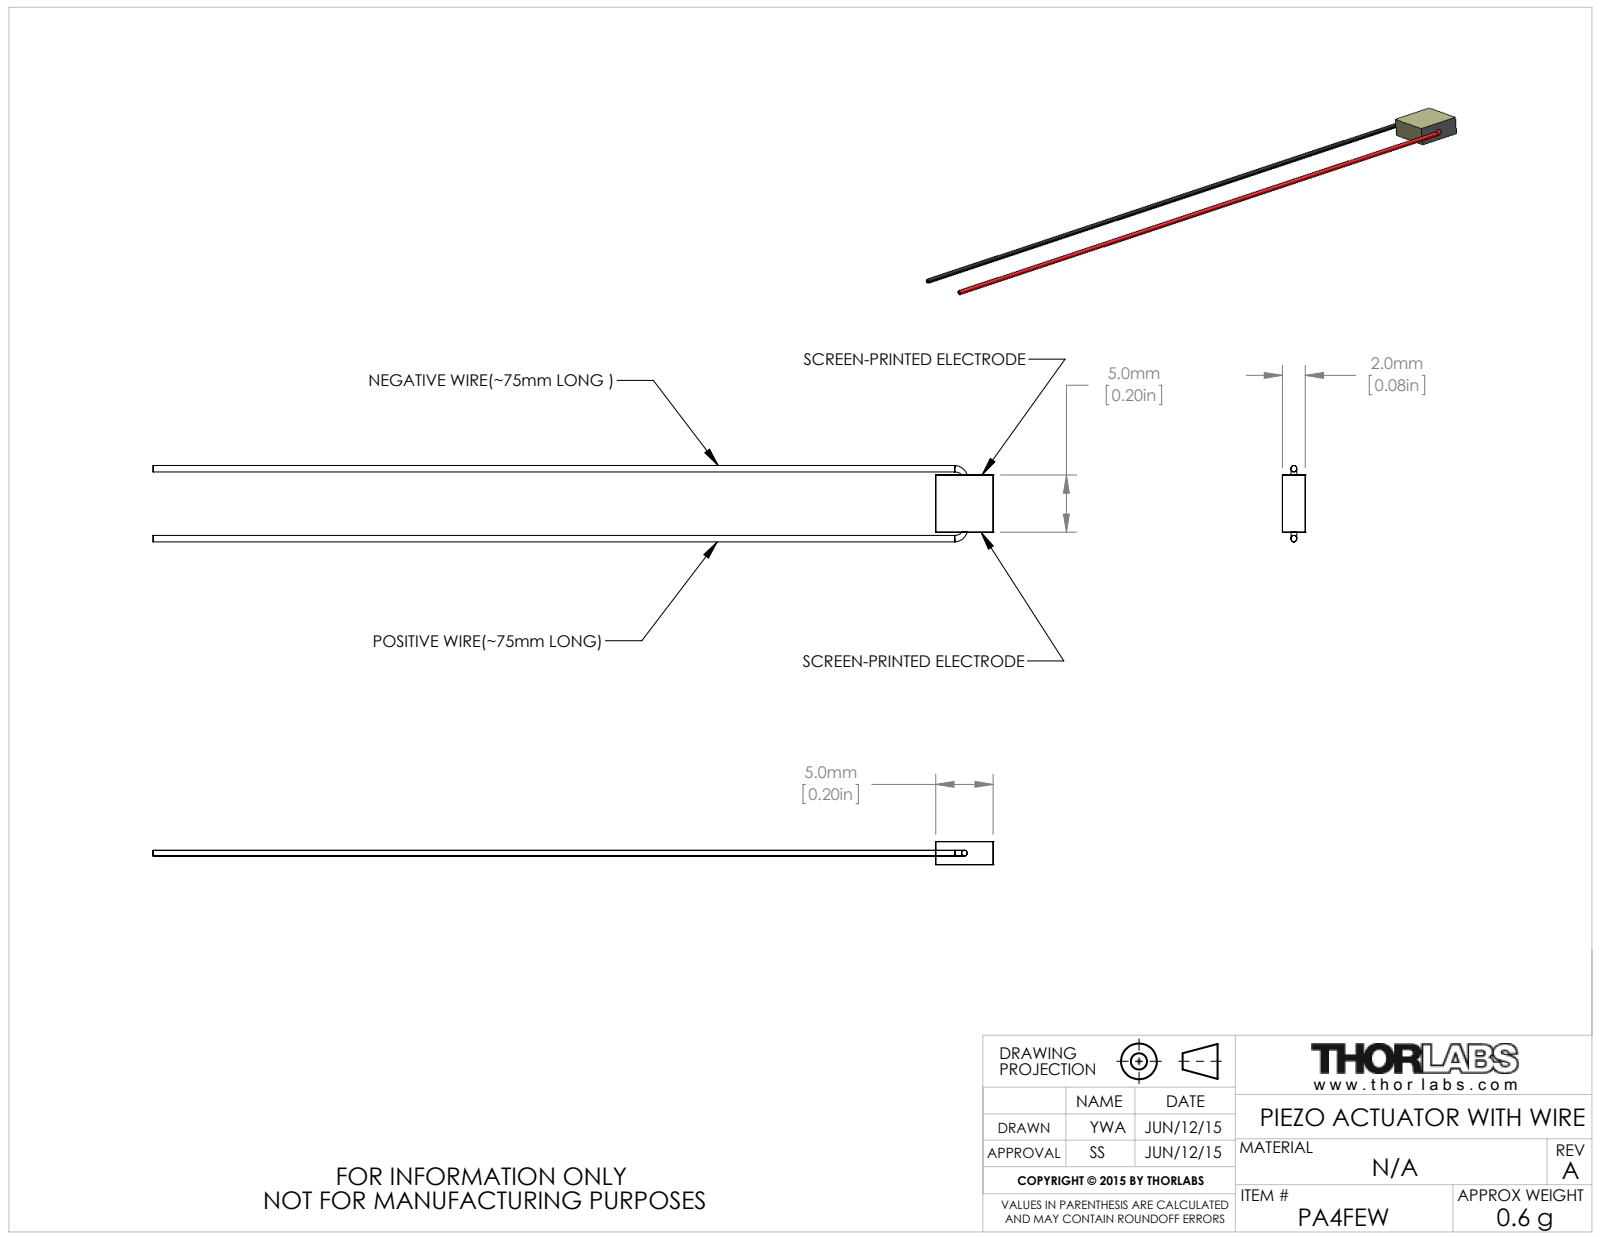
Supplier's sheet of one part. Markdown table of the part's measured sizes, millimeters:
| quantity | value |
| --- | --- |
| part name | CTN002586 |
| STEP written by | SolidWorks 2014 (AUTOMOTIVE_DESIGN) |
| units | millimeters |
| bodies | 1 solid, 16 faces (8 planar, 0 cylindrical, 8 other) |
| overall size | 73.34 × 6.67 × 2 |
| volume | 82 mm³ |
| surface area | 328 mm² |
| main face-to-face distances | 2, 5, 73.34, 68.34 |
